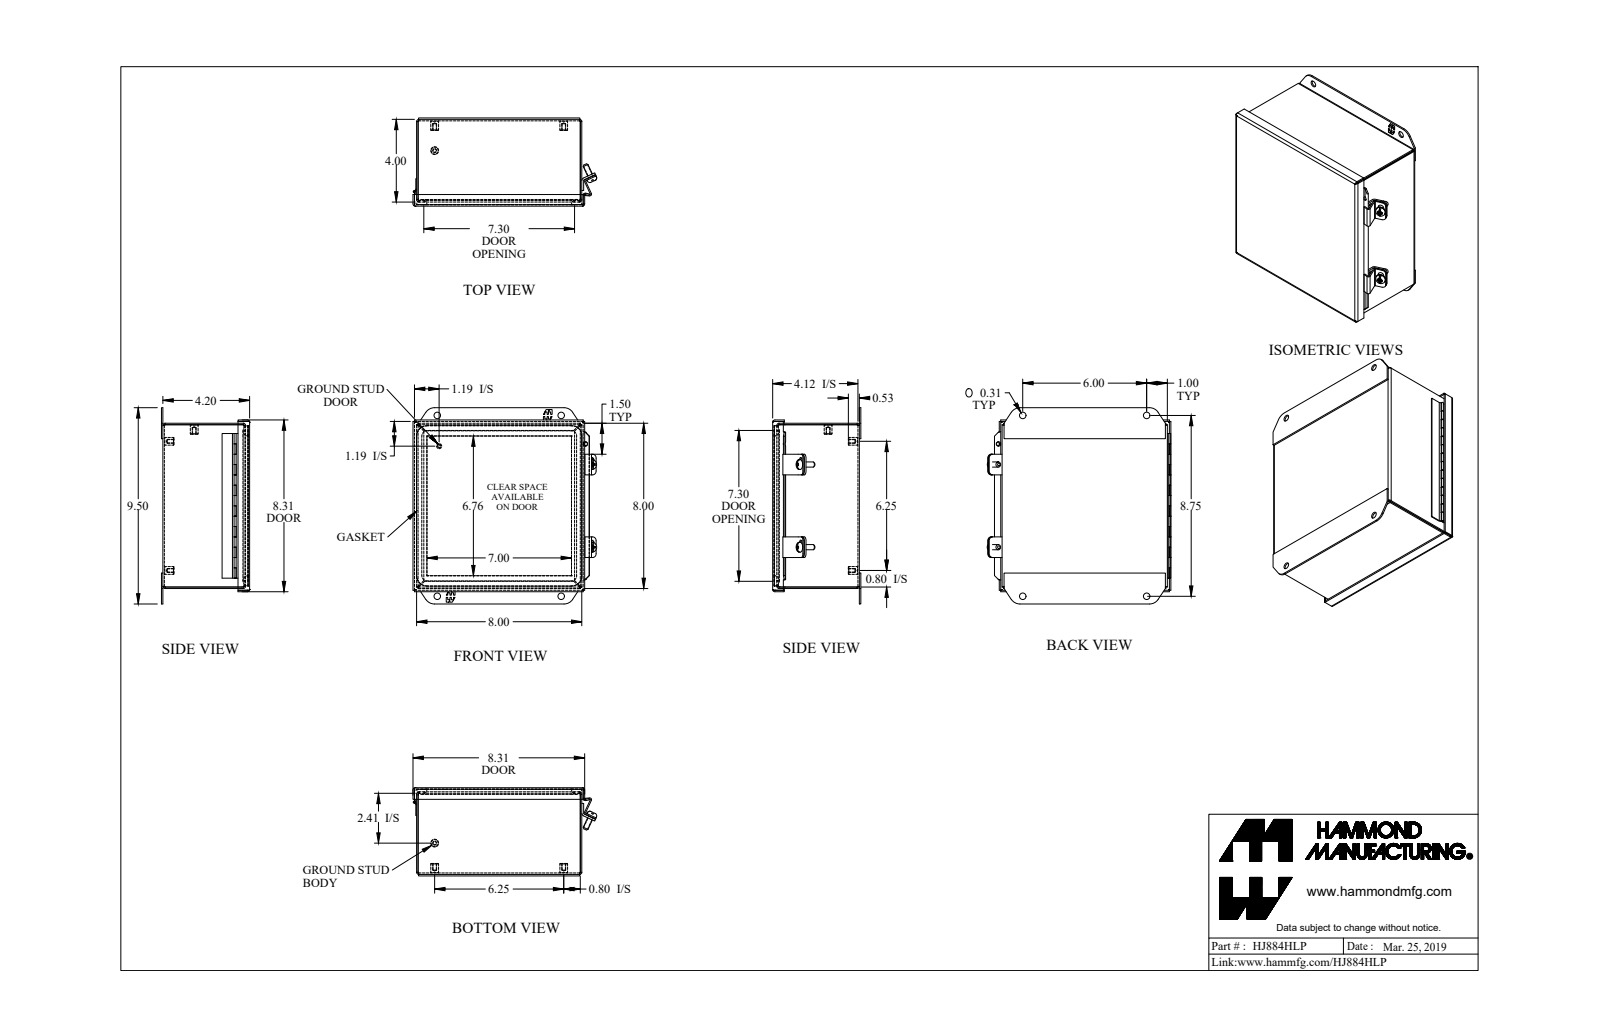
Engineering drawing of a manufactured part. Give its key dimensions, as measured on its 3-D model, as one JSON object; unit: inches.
{"part_name": "HJ884HLP", "step_written_by": "SolidWorks 2018 (AUTOMOTIVE_DESIGN)", "units": "inches", "bodies": {"solids": 20, "faces": 713, "planar": 382, "cylindrical": 203, "other": 128}, "overall_size": [9.5, 8.896, 4.269], "volume_in3": 25.65, "surface_area_in2": 721.9, "round_holes": [[0.156, 5], [0.313, 4], [0.213, 2], [0.05, 1]], "round_bosses_or_shafts": [[0.375, 5], [0.25, 3], [0.48, 2], [0.188, 1], [0.1, 1], [0.045, 1]], "partial_cylinders_radius": [[0.25, 16], [0.036, 13], [0.108, 13], [0.01, 4], [0.141, 4], [0.188, 4], [0.499, 4], [0.5, 4]], "face_to_face_distances": [0.072, 4.125, 7.928, 4.197, 8, 4.053, 7.856, 0.144, 4.269, 0.156], "hole_center_spacings": [6.25, 1.256, 1.256, 6, 6.251, 6.252, 7.501, 7.502]}
